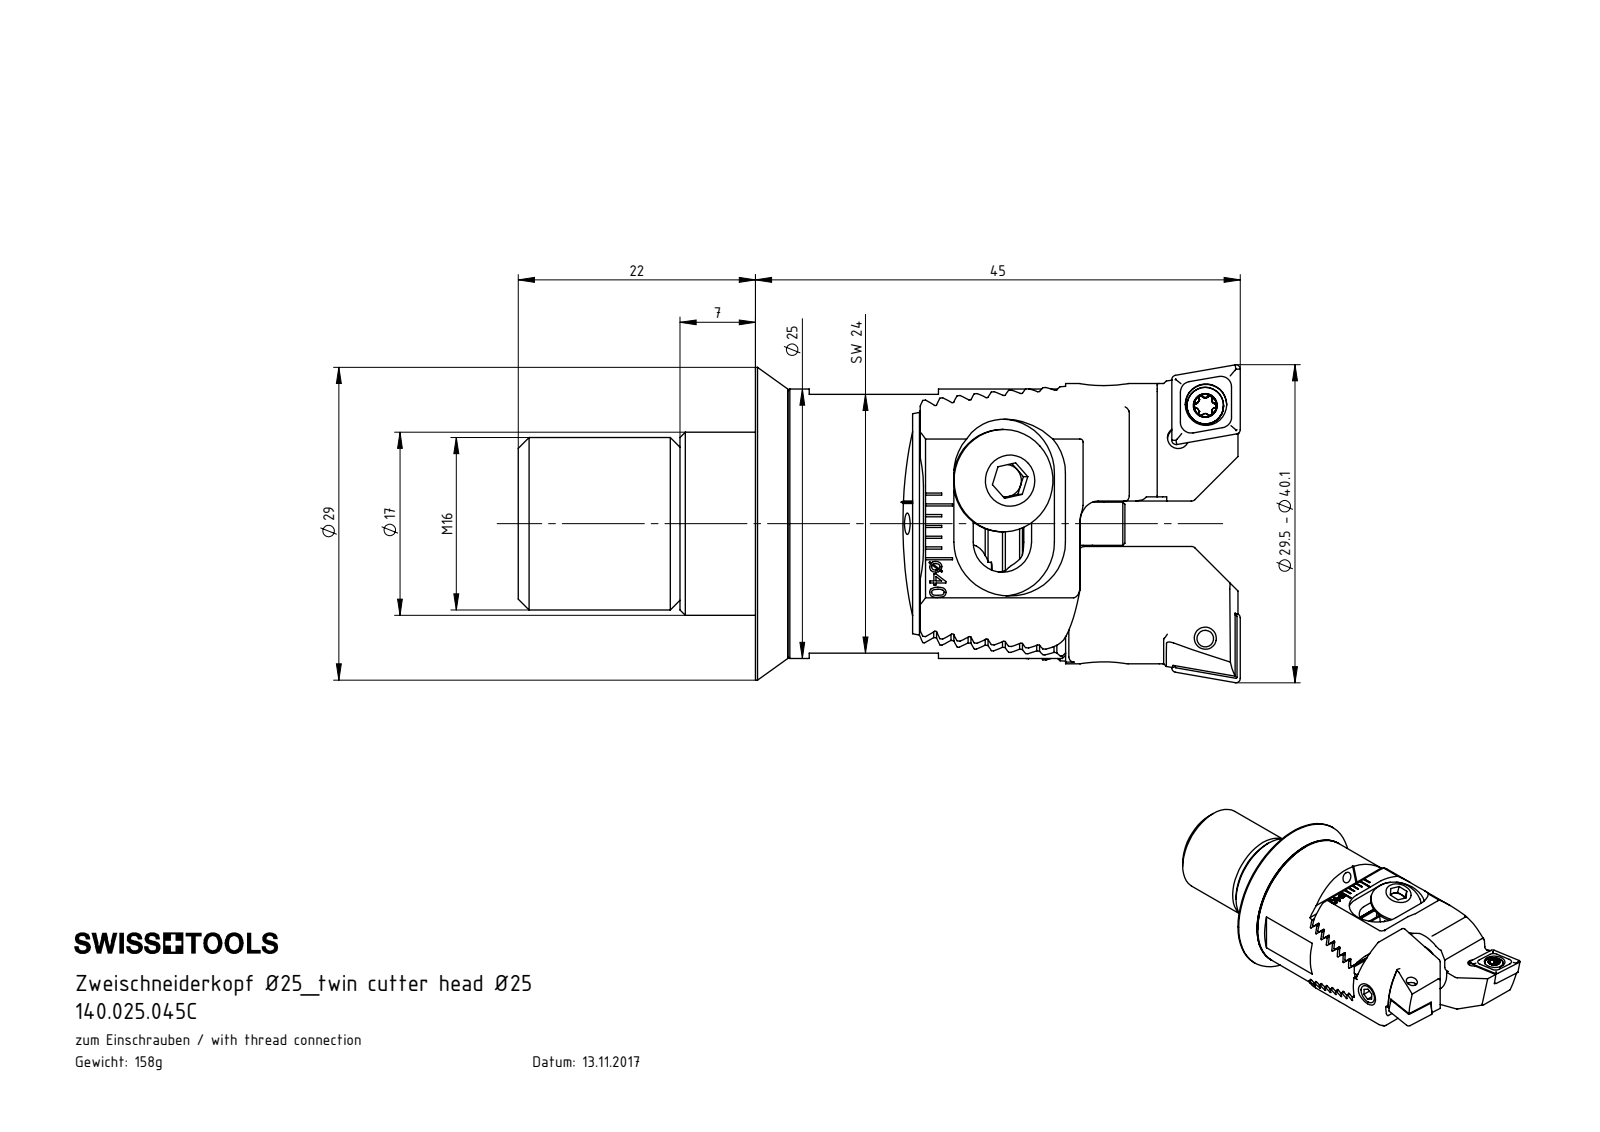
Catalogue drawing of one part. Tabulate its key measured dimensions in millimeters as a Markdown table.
| quantity | value |
| --- | --- |
| part name | Z25-ER1.002.012_A; Z25-ER3.001.010_A; WCA-ER2.001.006_B; ZC2-xxx.001.016_A (+8 more) |
| STEP written by | SolidWorks 2017 (CONFIG_CONTROL_DESIGN) |
| units | millimeters |
| bodies | 17 solids, 1044 faces (504 planar, 256 cylindrical, 284 other) |
| overall size | 67 × 29.5 × 29 |
| volume | 20 663 mm³ |
| surface area | 14 861 mm² |
| round holes (diameter × count) | 2 × 6, 1.6 × 2, 2.05 × 2, 2.8 × 2, 3.85 × 2, 4.2 × 2, 6 × 2, 2.5 × 1, 3.3 × 1, 3.5 × 1, 5.3 × 1, 10.6 × 1 |
| round bosses / shafts (diameter × count) | 9.5 × 2, 5 × 2, 4 × 2, 3.4 × 2, 2.5 × 2, 29 × 1, 28 × 1, 25 × 1 |
| partial cylindrical surfaces (radius × count) | 0.12 × 18, 0.5 × 18, 0.12 × 16, 0.21 × 12, 0.36 × 10, 2 × 4, 2.8 × 4, 5 × 4 |
| main face-to-face distances | 1.43, 3, 2.86, 7.14, 5.71, 1.39, 1.47, 8.57, 4.28, 10 |
| hole center spacings | 3.91, 4.01, 7, 19.06, 19.15, 21.97, 13.52, 15.9 |
